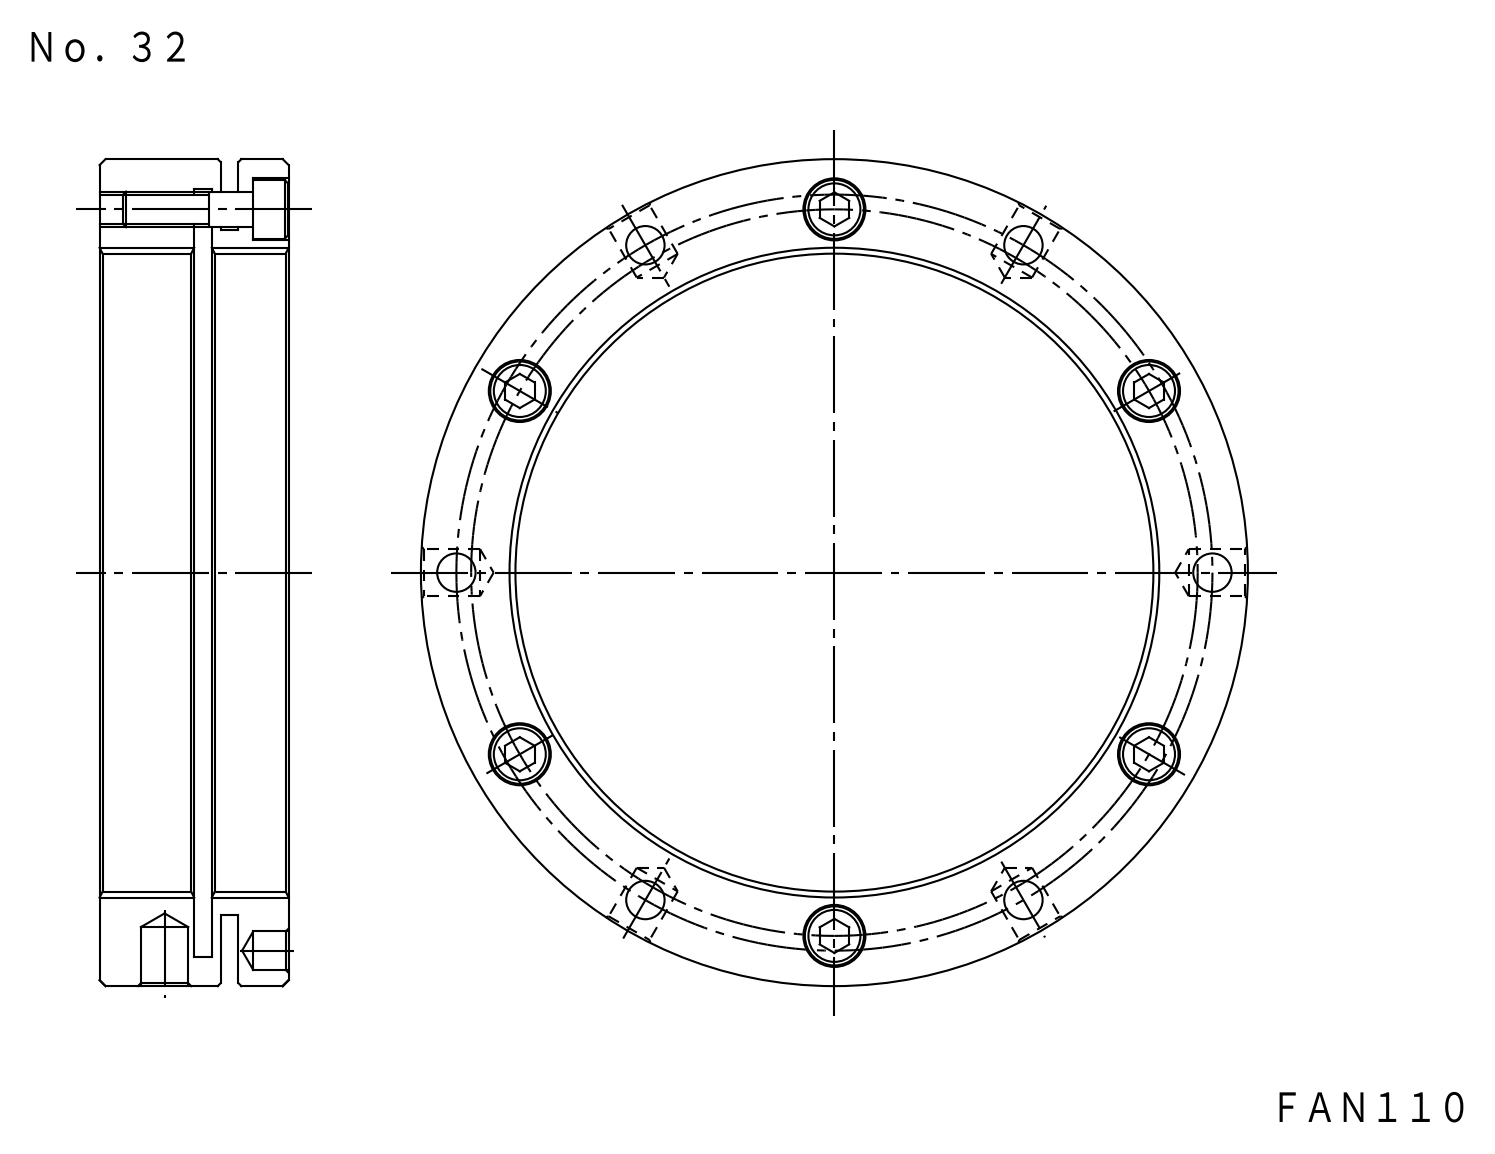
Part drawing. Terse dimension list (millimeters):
name: FKD FAN110; M6X22_default
written by: SolidWorks 2012 (CONFIG_CONTROL_DESIGN)
unit: mm
bodies: 7 solids, 204 faces (72 planar, 108 cylindrical, 24 other)
size: 140 × 140 × 32
volume: 163 337 mm³; area: 63 294 mm²
holes: 6× ⌀6.3, 6× ⌀6.5, 6× ⌀10.5, 4× ⌀4.92, 3× ⌀8, 2× ⌀4.92, 1× ⌀110, 1× ⌀133
bosses: 6× ⌀10, 6× ⌀6, 1× ⌀140, 1× ⌀119
face distances: 2.5, 4, 32, 17, 15, 19.5, 12.5, 21, 1.5, 11
hole spacings: 63, 64, 89.81, 32.88, 122.68, 109.12, 32.89, 110.85
